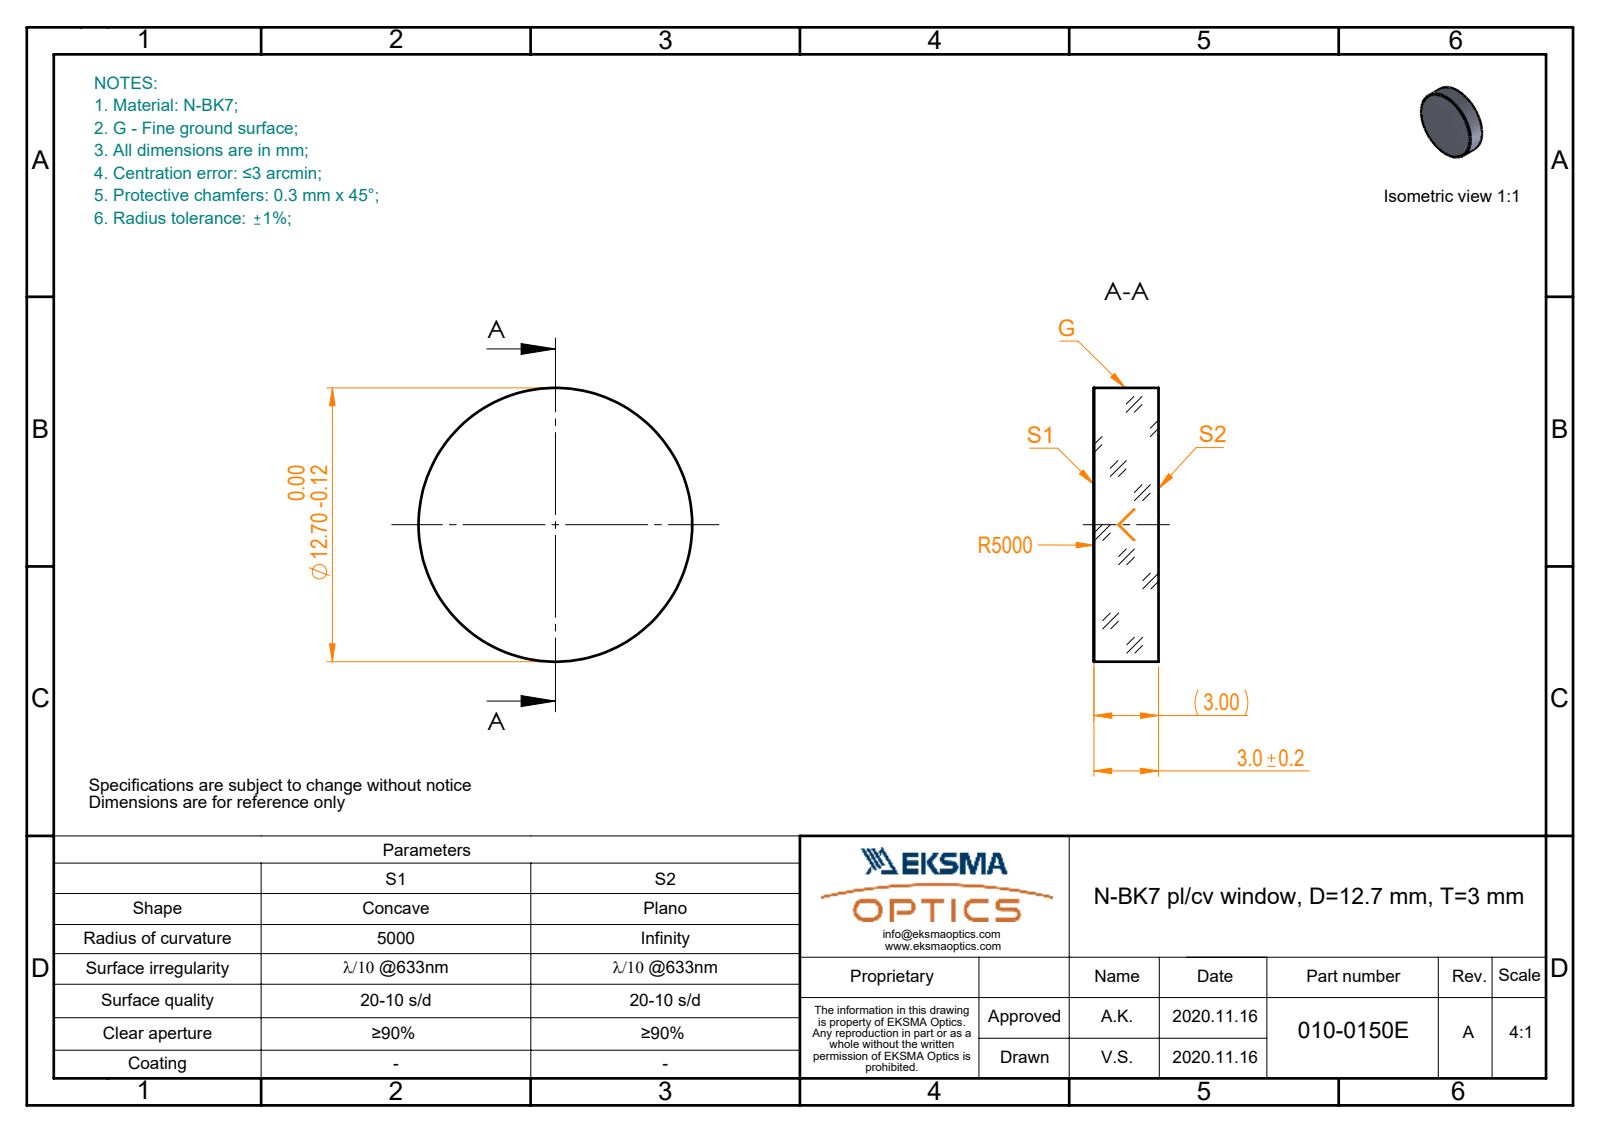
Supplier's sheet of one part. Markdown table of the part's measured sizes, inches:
| quantity | value |
| --- | --- |
| part name | 010-0150E_N-BK7_PCV_window |
| STEP written by | SolidWorks 2019 (CONFIG_CONTROL_DESIGN) |
| units | inches |
| bodies | 1 solid, 5 faces (1 planar, 2 cylindrical, 2 other) |
| overall size | 0.5 × 0.5 × 0.118 |
| volume | 0.023 in³ |
| surface area | 0.578 in² |
| round bosses / shafts (diameter × count) | 0.5 × 1 |
